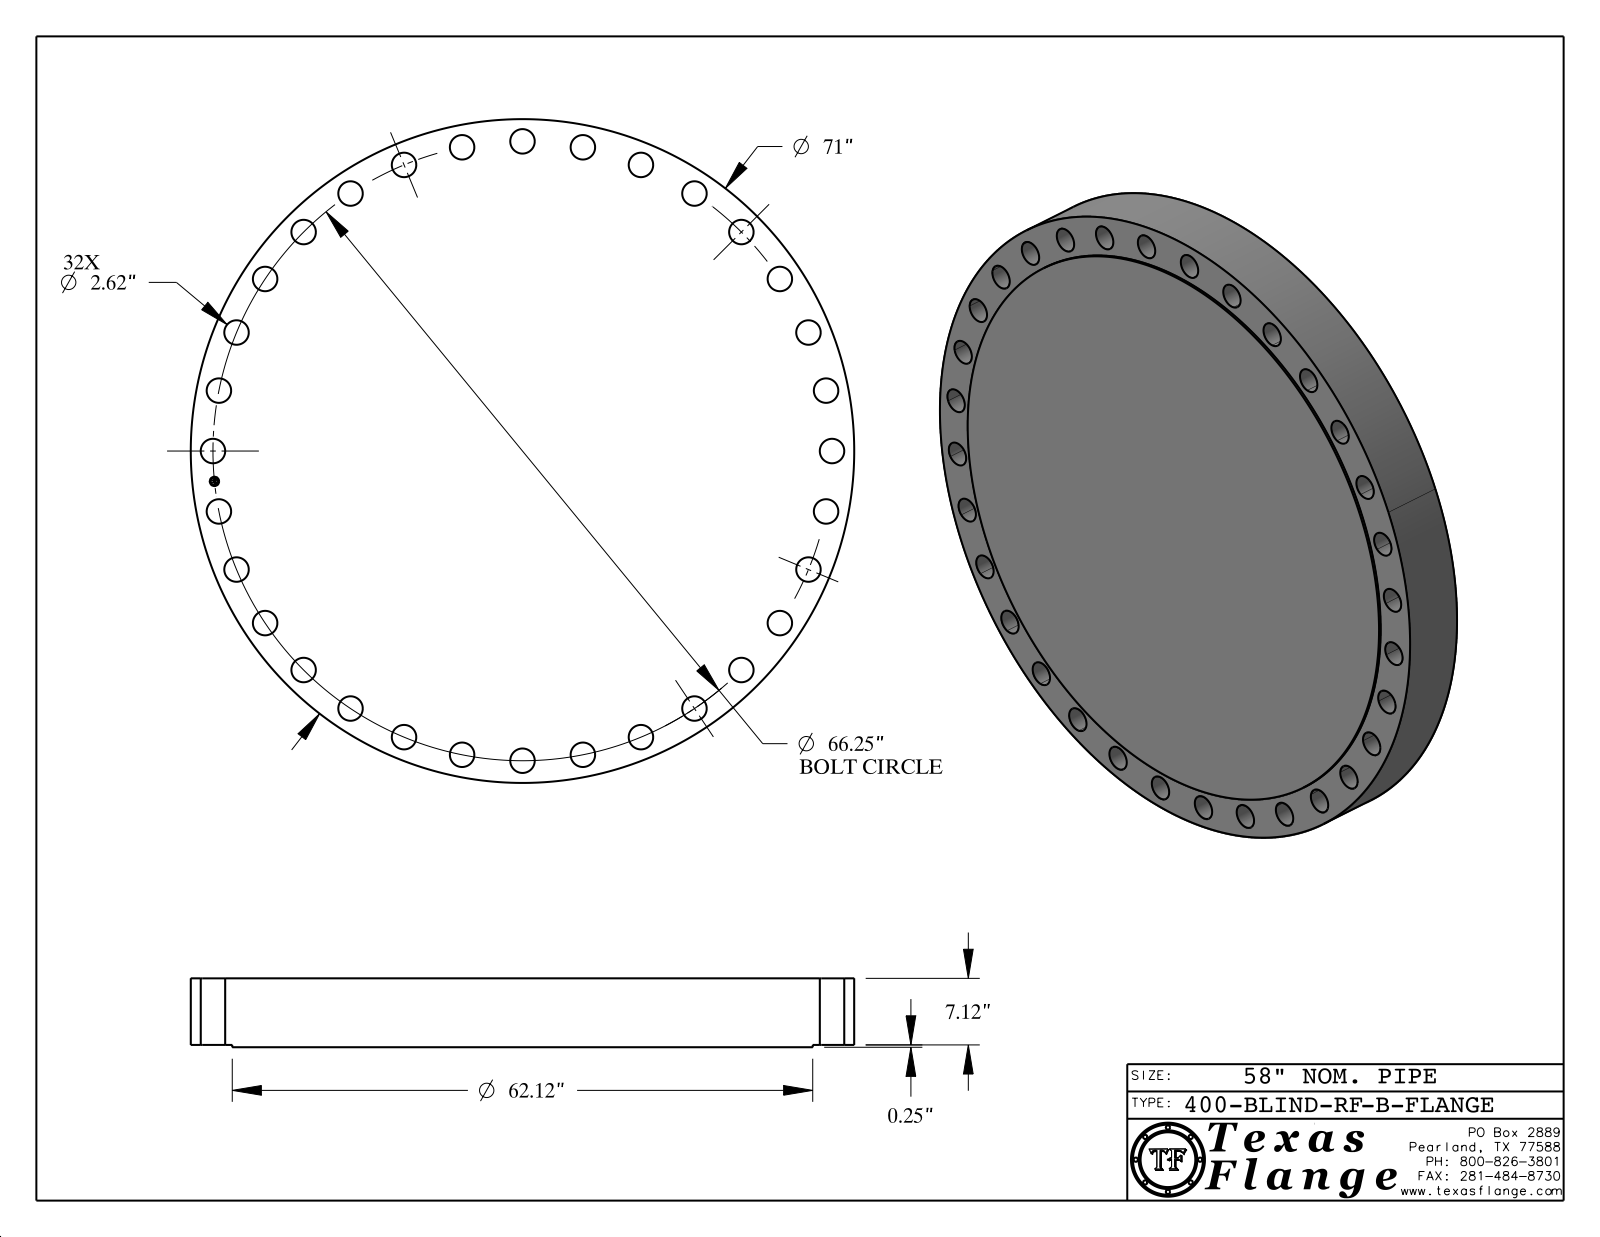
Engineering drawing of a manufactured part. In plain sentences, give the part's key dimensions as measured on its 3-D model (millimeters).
The part is named "400-BLIND-RF, Series B". Its 3-D file was written by "CATIA V5 STEP AP214 (AUTOMOTIVE_DESIGN)". It is 1 solid with 456 faces: 368 planar, 88 cylindrical and 0 other. Overall it measures 1803.4 by 1803.4 by 187.2 millimeters. Its volume is 454 200 000 cubic millimeters and its surface area 7 152 000 square millimeters. Round holes: 32 of diameter 66.5, 1 of diameter 25.4. Round bosses or shafts: 8 of diameter 1.5, 1 of diameter 1803.4, 1 of diameter 1577.8, 1 of diameter 20. The main face-to-face distances are 187.2, 6.4, 180.8, 0.4, 186.8, 180.5, 7.6, 7.4, 1.4, 4.9. The hole center spacings are 1554.7, 164.9, 1610.3, 328.3, 1674.6, 1189.9, 1650.4, 1399.2.
